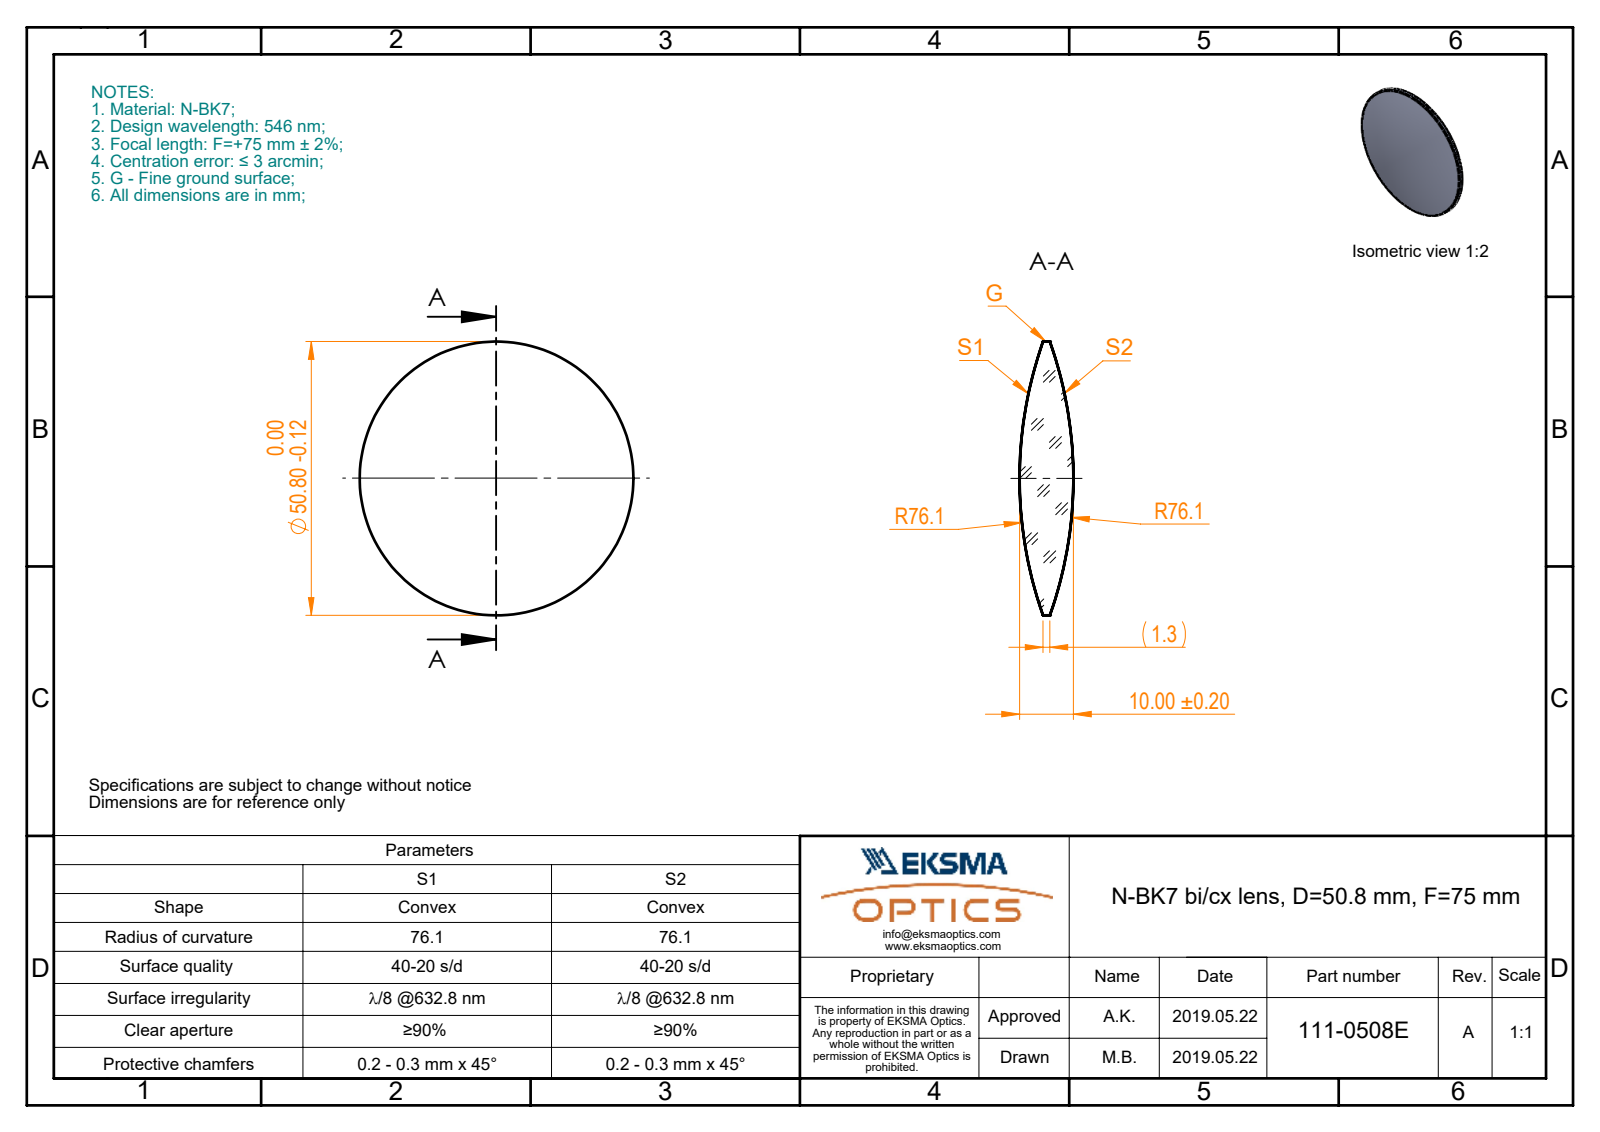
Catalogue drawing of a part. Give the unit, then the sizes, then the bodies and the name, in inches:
Units: inches
Overall size (bounding box): 2 × 2 × 0.394
Round bosses / shafts (diameter × count): ⌀2 ×1
Volume: 0.702 in³ · Surface area: 6.783 in²
Bodies: 1 solid, 6 faces (0 planar, 2 cylindrical, 4 other)
Part name (STEP PRODUCT): 111-0508E BK7 bi-cx 50.8 F75
STEP written by: SolidWorks 2017 (CONFIG_CONTROL_DESIGN)
